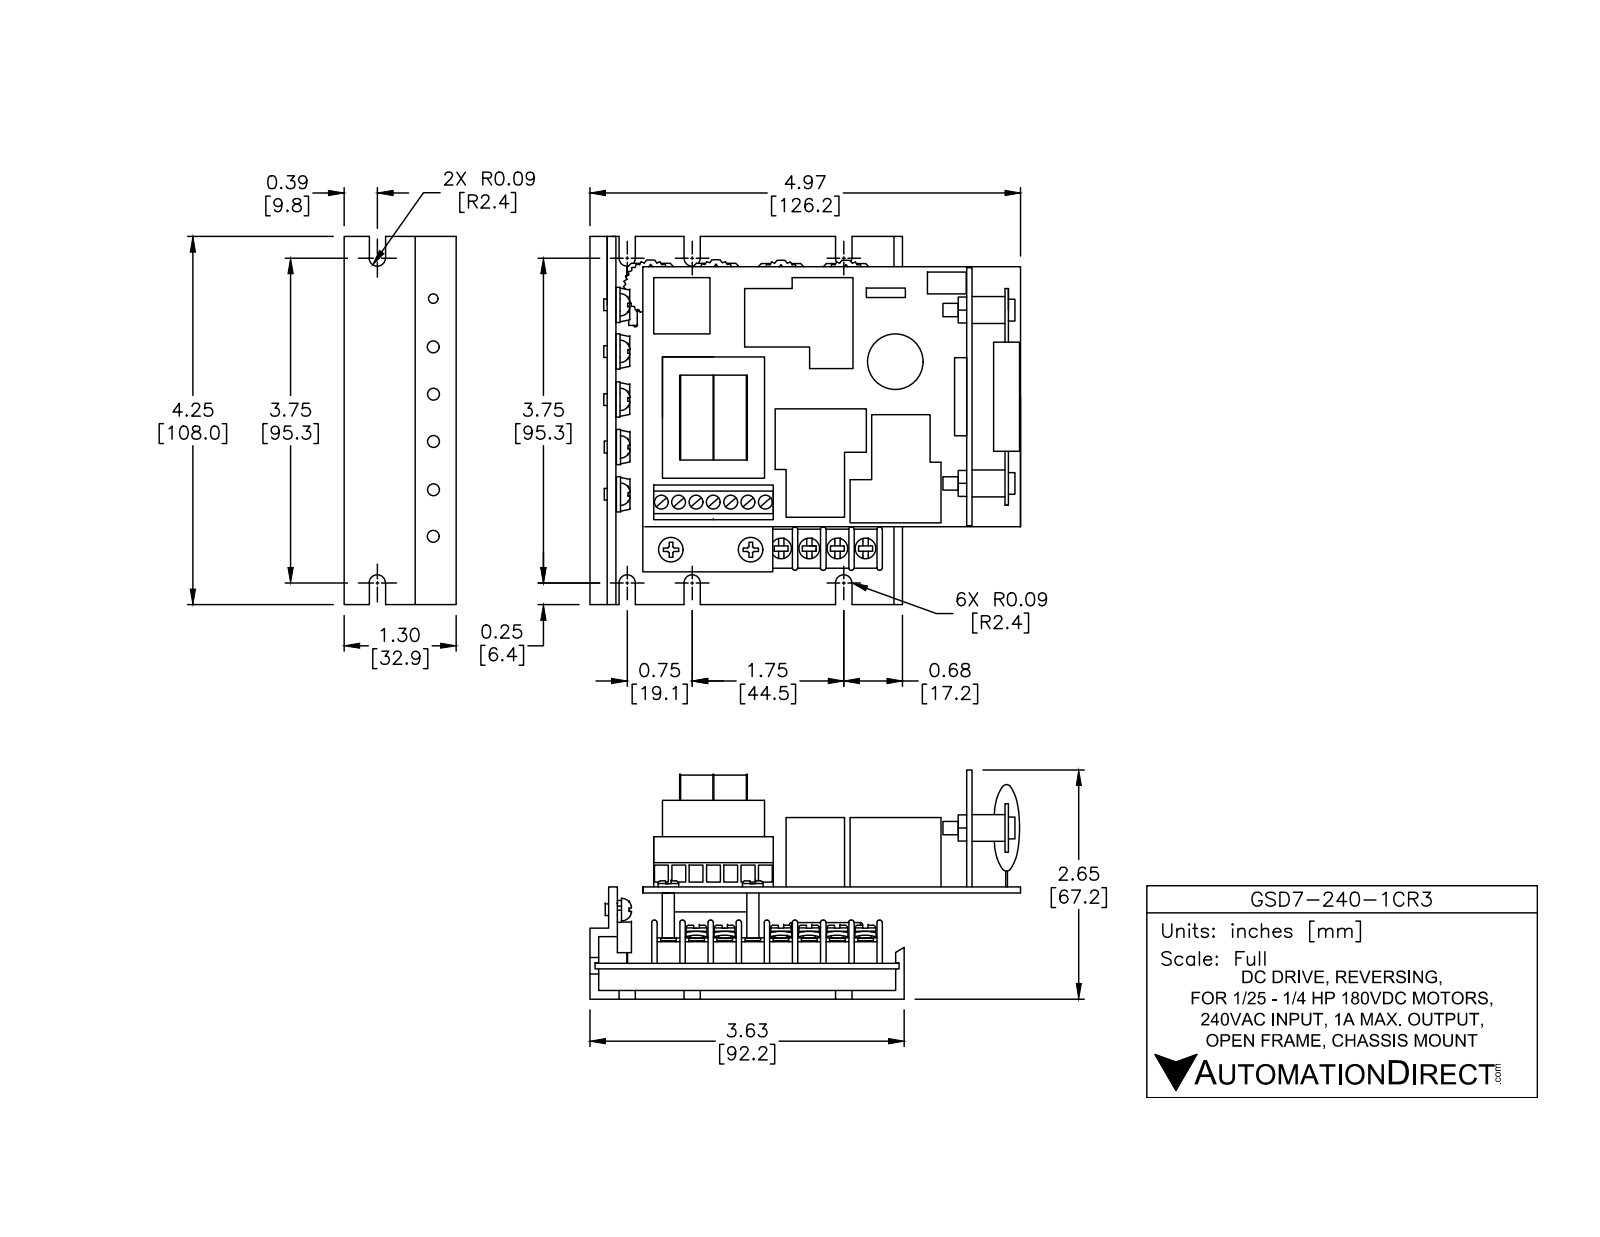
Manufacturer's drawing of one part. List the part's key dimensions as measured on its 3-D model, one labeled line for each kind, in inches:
Part name (STEP PRODUCT): R1; HDS6TB.4375Z; C9; CAP_AXIAL_16.51S-4D-4.1H (+8 more)
STEP written by: SolidWorks 2014 (AUTOMOTIVE_DESIGN)
Units: inches
Bodies: 99 solids, 5316 faces (2781 planar, 1893 cylindrical, 642 other)
Overall size (bounding box): 5.227 × 4.25 × 2.527
Volume: 11.08 in³ · Surface area: 213.3 in²
Round holes (diameter × count): ⌀0.033 ×90, ⌀0.043 ×19, ⌀0.035 ×16, ⌀0.046 ×12, ⌀0.07 ×9, ⌀0.035 ×8, ⌀0.09 ×7, ⌀0.147 ×7, ⌀0.04 ×6, ⌀0.11 ×6, ⌀0.144 ×5, ⌀0.111 ×4
Round bosses / shafts (diameter × count): ⌀0.025 ×43, ⌀0.024 ×30, ⌀0.025 ×22, ⌀0.107 ×20, ⌀0.081 ×19, ⌀0.08 ×19, ⌀0.03 ×16, ⌀0.019 ×12
Partial cylindrical surfaces — rounded edges, fillets, slot ends (radius × count): R0.005 ×23, R0.02 ×12, R0.062 ×12, R0.04 ×11, R0.024 ×10, R0.075 ×8, R0.094 ×8, R0.05 ×6
Main face-to-face distances: 0.1, 0.065, 1.127, 1.227, 0.25, 0.312, 0.75, 1.062, 1.162, 0.815
Hole centre spacings: 0.2, 0.55, 0.1, 0.4, 0.461, 0.751, 0.636, 0.8
